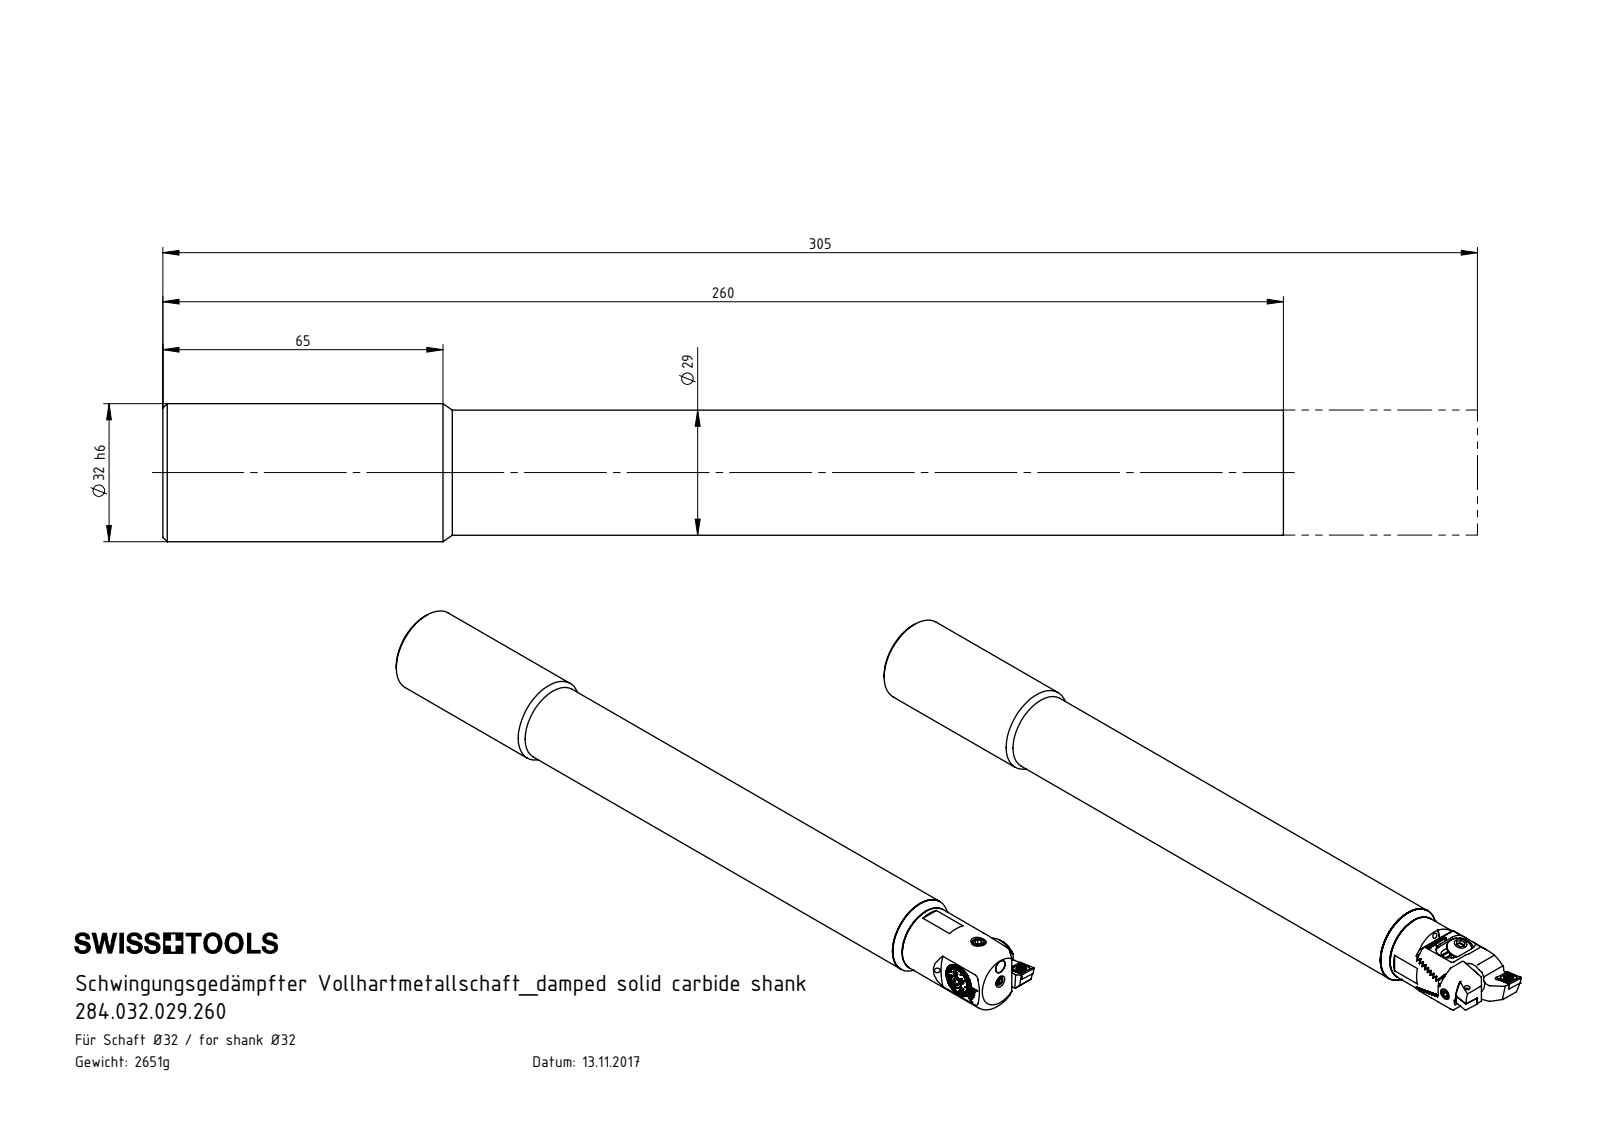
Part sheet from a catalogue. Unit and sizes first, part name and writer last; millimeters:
Units: millimetres
Overall size (bounding box): 305 × 32 × 32
Round holes (diameter × count): ⌀2 ×5, ⌀4.2 ×3, ⌀2.05 ×2, ⌀2.1 ×1, ⌀2.4 ×1, ⌀2.7 ×1, ⌀2.8 ×1, ⌀3 ×1, ⌀3.3 ×1, ⌀3.85 ×1, ⌀5 ×1, ⌀5.5 ×1
Round bosses / shafts (diameter × count): ⌀5 ×2, ⌀4.95 ×2, ⌀2.5 ×2, ⌀32 ×1, ⌀29 ×1, ⌀25 ×1, ⌀16 ×1, ⌀12.98 ×1
Partial cylindrical surfaces — rounded edges, fillets, slot ends (radius × count): R0.21 ×6, R0.36 ×5, R0.5 ×4, R1.32 ×2, R0.2 ×1, R0.36 ×1, R1.05 ×1, R1.25 ×1
Main face-to-face distances: 260, 3, 224, 36, 263, 39, 302.15, 78.15, 42.15, 39.15
Hole centre spacings: 3.84, 3.99, 4.48, 6.8, 9.46, 16.65
Volume: 195 471 mm³ · Surface area: 49 652 mm²
Bodies: 22 solids, 878 faces (372 planar, 172 cylindrical, 334 other)
Part name (STEP PRODUCT): F25-BG1.009.006_A; F25-BG2.008.009_A; HP5-ER1.019.036_A; U32-HP5.029.260_A (+8 more)
STEP written by: SolidWorks 2017 (CONFIG_CONTROL_DESIGN)
